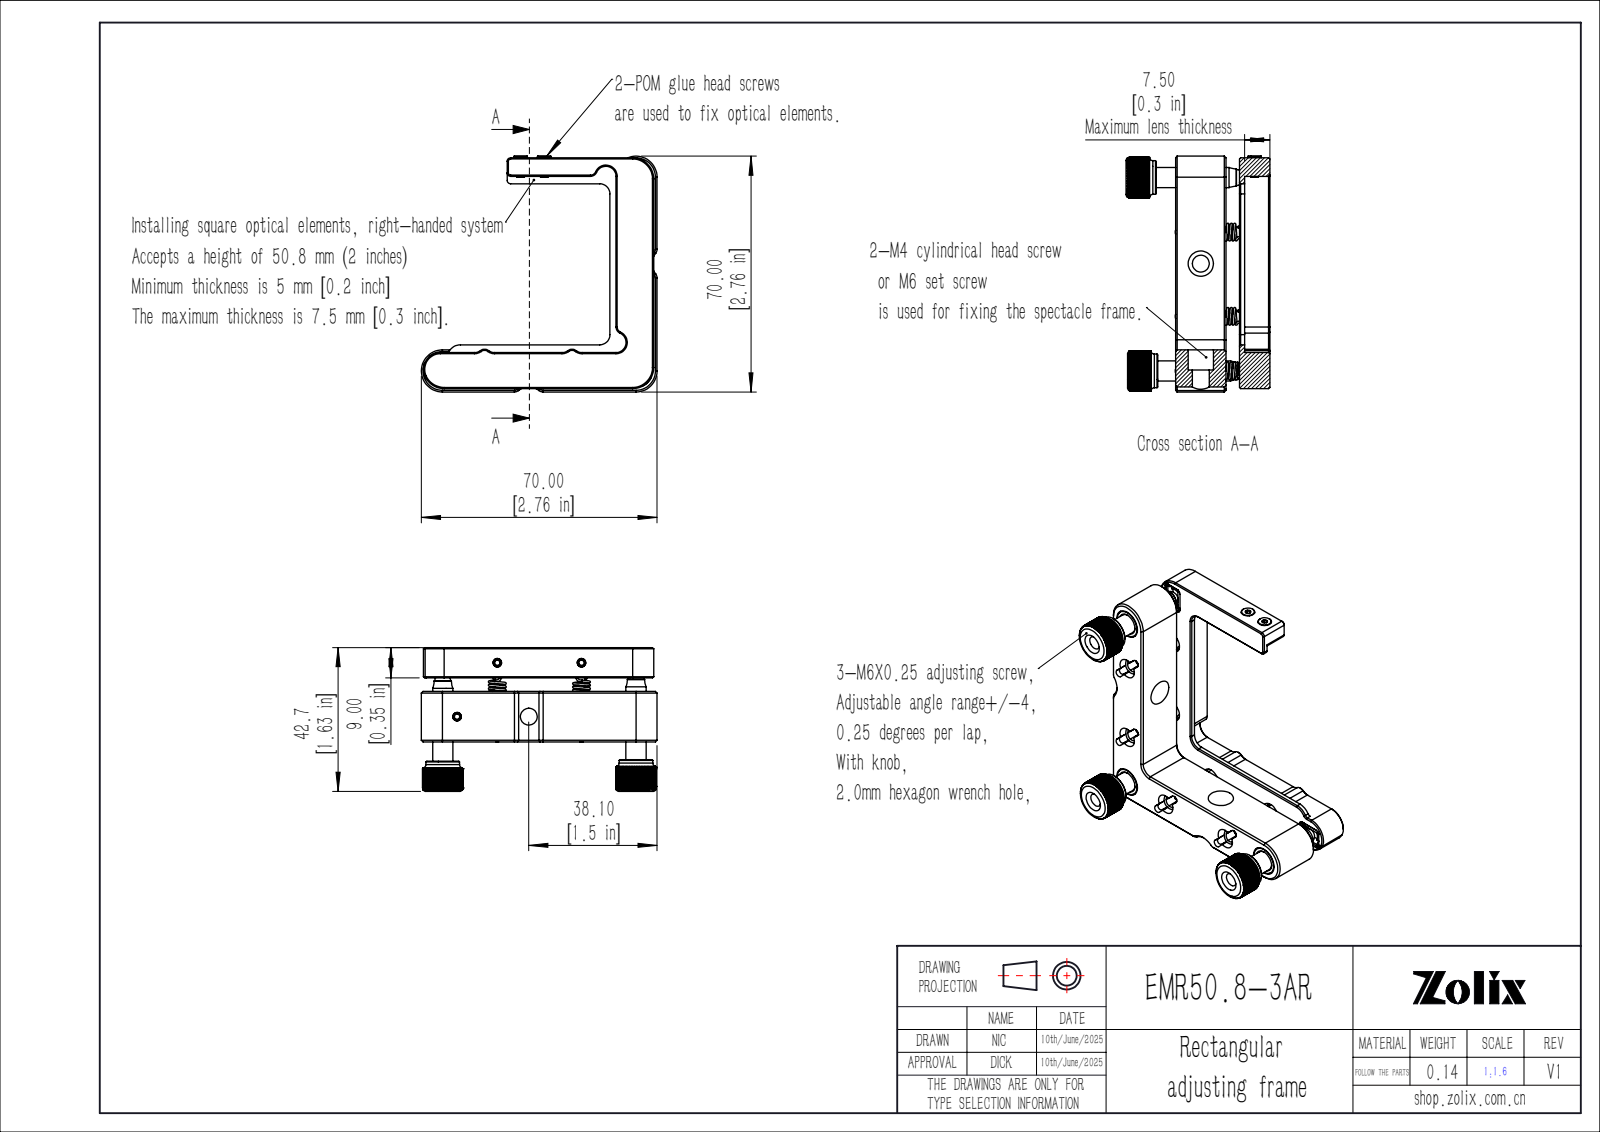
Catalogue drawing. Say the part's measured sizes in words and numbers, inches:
The part is named "EMR50.8-3AR". Its 3-D file was written by "SolidWorks 2020 (CONFIG_CONTROL_DESIGN)". It is 0 solids with 1269 faces: 654 planar, 362 cylindrical and 253 other. Overall it measures 2.756 by 2.756 by 1.681 inches. Round holes: 6 of diameter 0.236, 3 of diameter 0.339, 3 of diameter 0.386, 2 of diameter 0.13, 2 of diameter 0.157, 2 of diameter 0.197, 2 of diameter 0.295, 1 of diameter 0.394. Round bosses or shafts: 4 of diameter 0.079, 4 of diameter 0.059, 3 of diameter 0.157, 2 of diameter 0.394, 2 of diameter 0.094, 1 of diameter 0.236, 1 of diameter 0.118. Partial cylindrical surfaces (rounded edges, fillets, slot ends): 9 of radius 0.118, 8 of radius 0.031, 8 of radius 0.043, 8 of radius 0.079, 6 of radius 0.246, 4 of radius 0.039, 3 of radius 0.236, 2 of radius 0.098. The main face-to-face distances are 0.354, 0.492, 0.512, 0.157, 0.591, 1.102, 0.748, 0.039, 0.453, 0.217. The hole center spacings are 0.638, 1.622, 0.984, 1.743, 2.26, 2.348, 2.782, 0.276.
